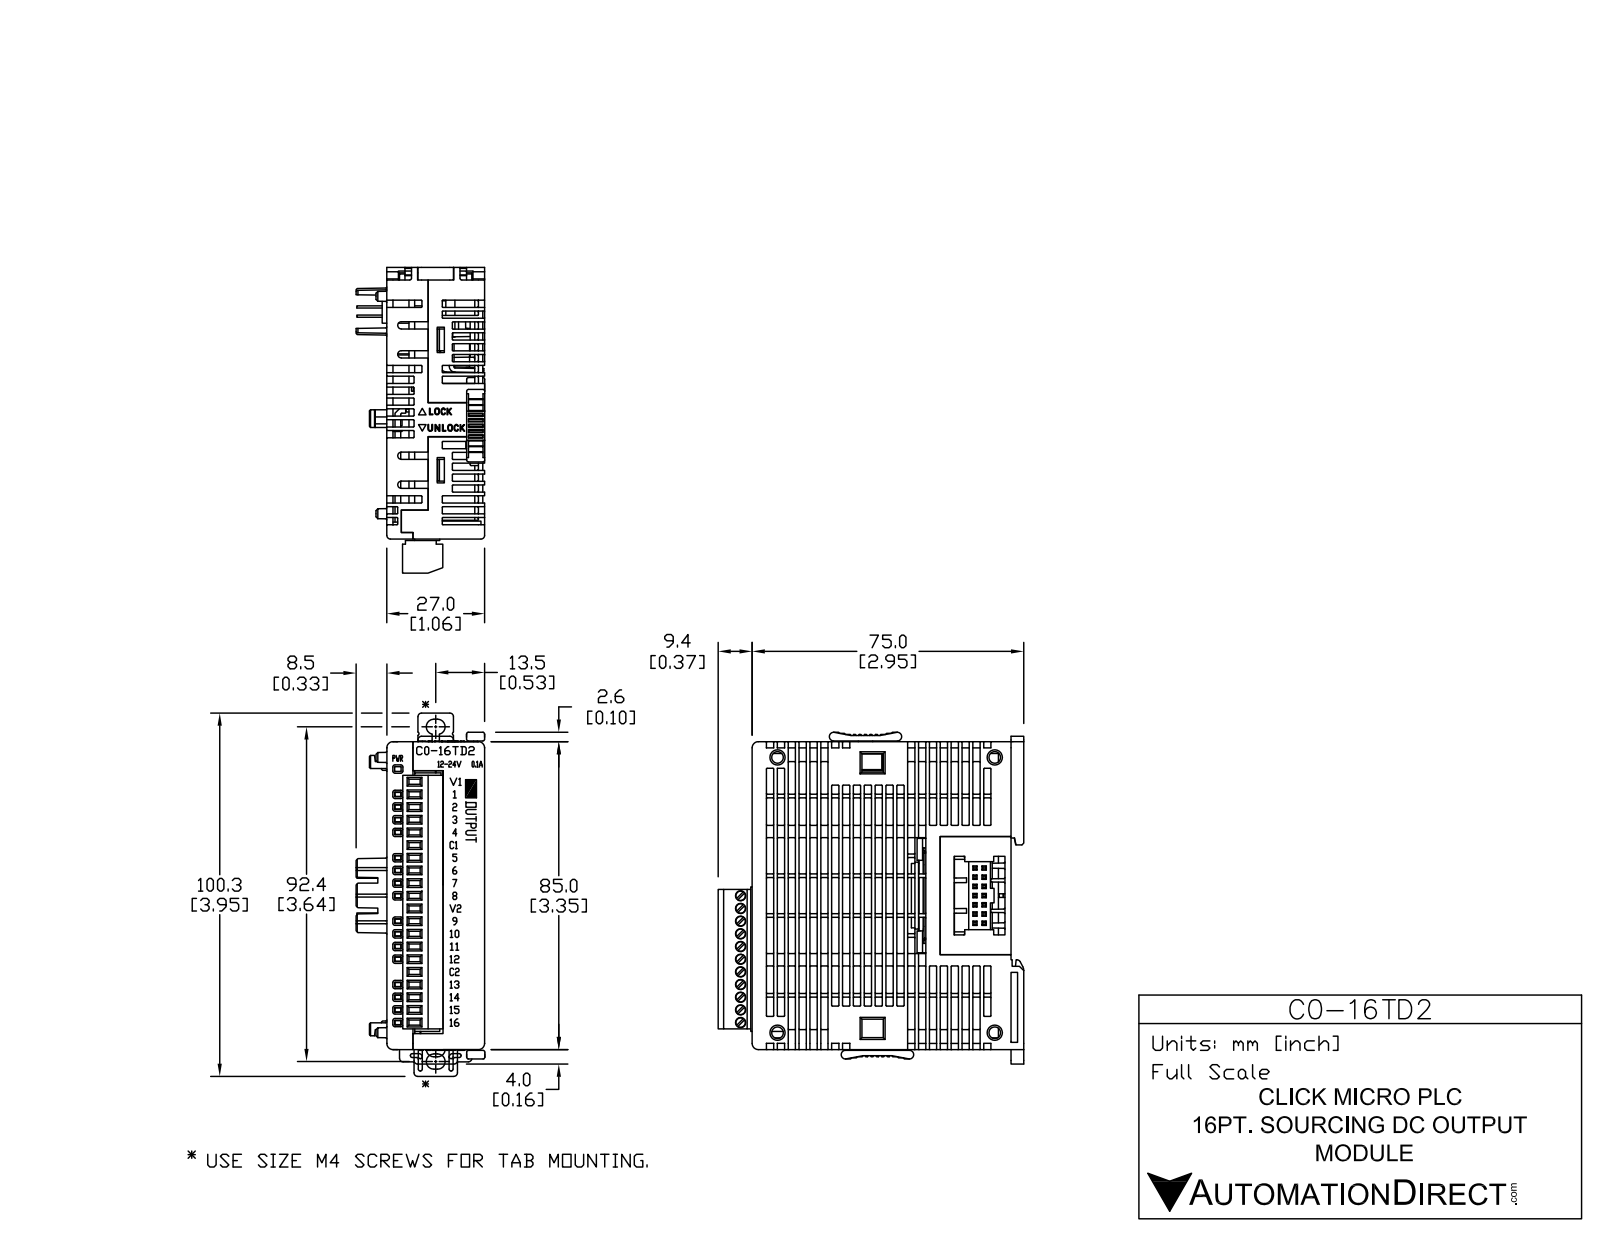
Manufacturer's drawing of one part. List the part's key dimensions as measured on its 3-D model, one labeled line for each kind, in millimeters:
Part name (STEP PRODUCT): C0-16TD2
STEP written by: SolidWorks 2009 (AUTOMOTIVE_DESIGN)
Units: millimetres
Bodies: 1 solid, 3989 faces (2836 planar, 1037 cylindrical, 116 other)
Overall size (bounding box): 91.6 × 84.4 × 35.55
Volume: 165 090 mm³ · Surface area: 33 615 mm²
Round holes (diameter × count): ⌀1 ×20, ⌀2.8 ×20, ⌀3.2 ×4, ⌀2 ×2
Round bosses / shafts (diameter × count): ⌀2.6 ×20, ⌀1.9 ×1
Partial cylindrical surfaces — rounded edges, fillets, slot ends (radius × count): R0.2 ×570, R0.5 ×43, R0.3 ×22, R2.8 ×20, R1 ×18, R1.2 ×12, R1.7 ×6, R2.1 ×4
Main face-to-face distances: 0.5, 27.01, 0.51, 26.5, 71.5, 85, 1.7, 26.3, 26.81, 3.5
Hole centre spacings: 3.5, 7, 10.5, 14, 17.5, 21, 24.5, 28
